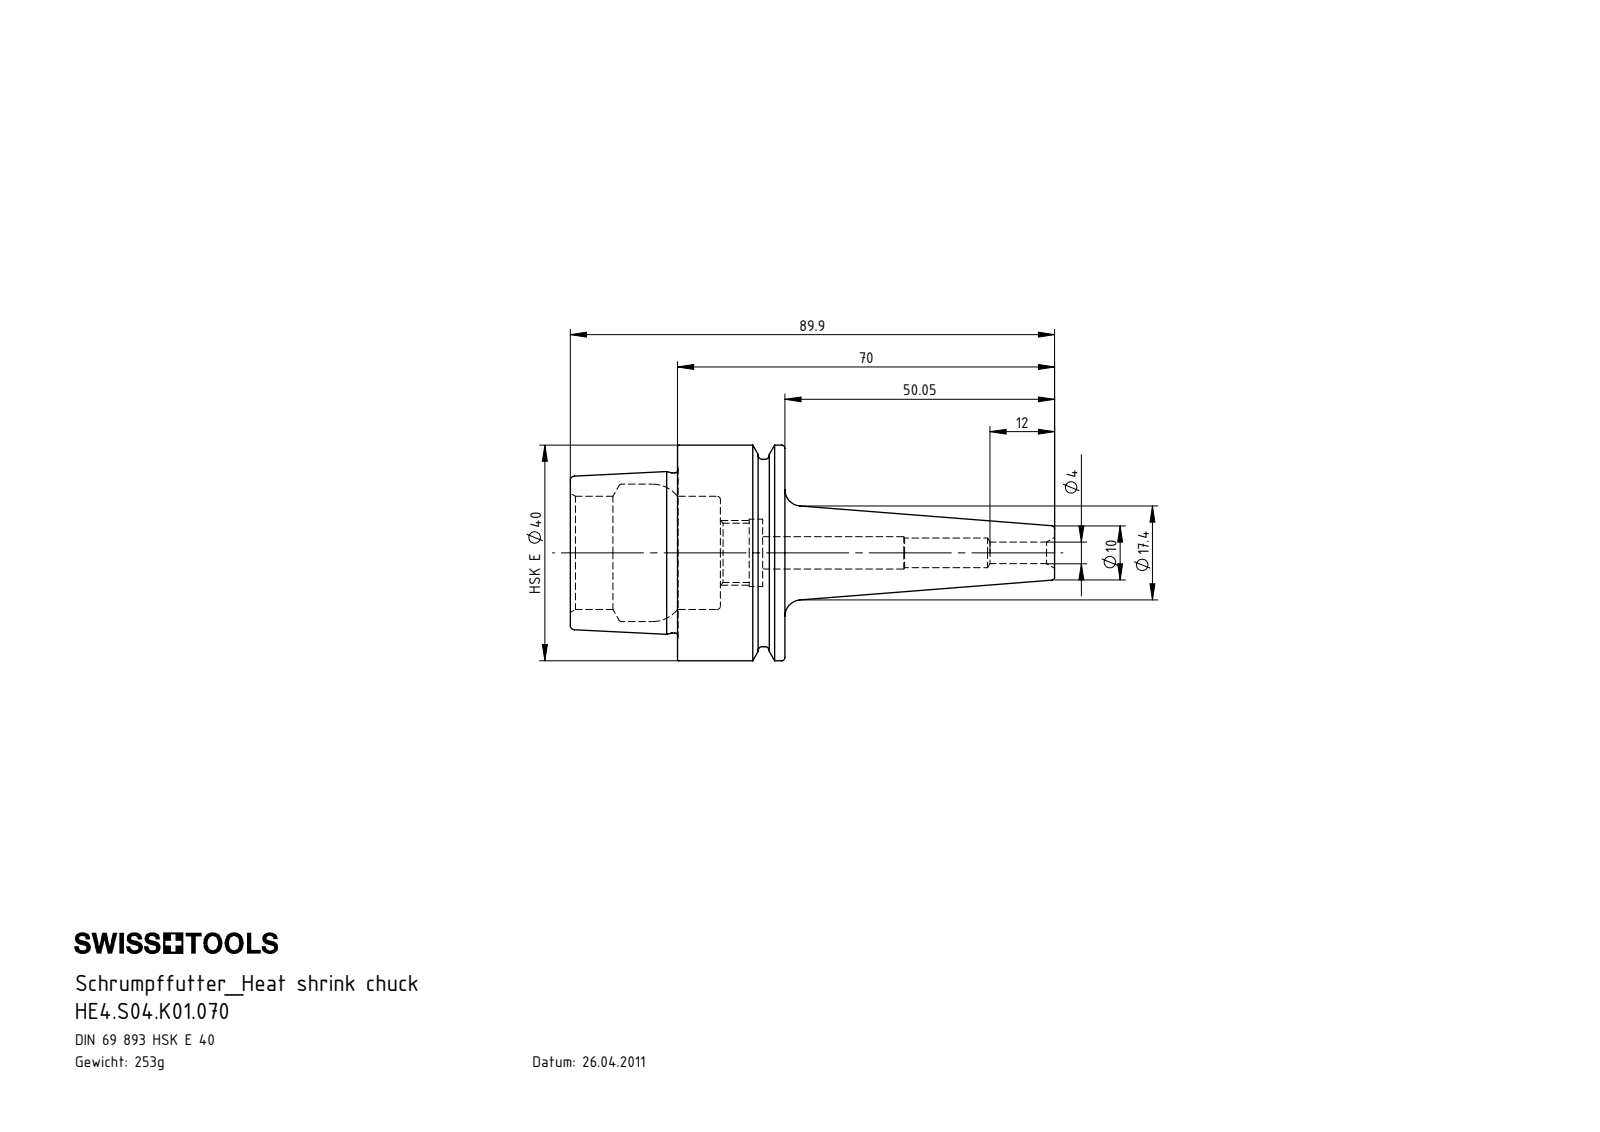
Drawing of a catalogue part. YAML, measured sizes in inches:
part_name: "HE4.S04.K01.070"
step_written_by: "SolidWorks 2017 (CONFIG_CONTROL_DESIGN)"
units: inches
bodies: {solids: 1, faces: 81, planar: 9, cylindrical: 24, other: 48}
overall_size: [3.539, 1.575, 1.575]
volume: 1.969
surface_area: 19.04
round_holes:
  - {diameter: 0.157, count: 1}
  - {diameter: 0.217, count: 1}
  - {diameter: 0.236, count: 1}
  - {diameter: 0.433, count: 1}
  - {diameter: 0.492, count: 1}
  - {diameter: 0.827, count: 1}
  - {diameter: 1.004, count: 1}
round_bosses_or_shafts:
  - {diameter: 1.575, count: 1}
  - {diameter: 1.368, count: 1}
  - {diameter: 1.17, count: 1}
face_to_face_distances: [0.785, 0.313, 0.472, 0.783, 1.096, 1.569, 1.406, 0.622, 0.309, 0.163]
